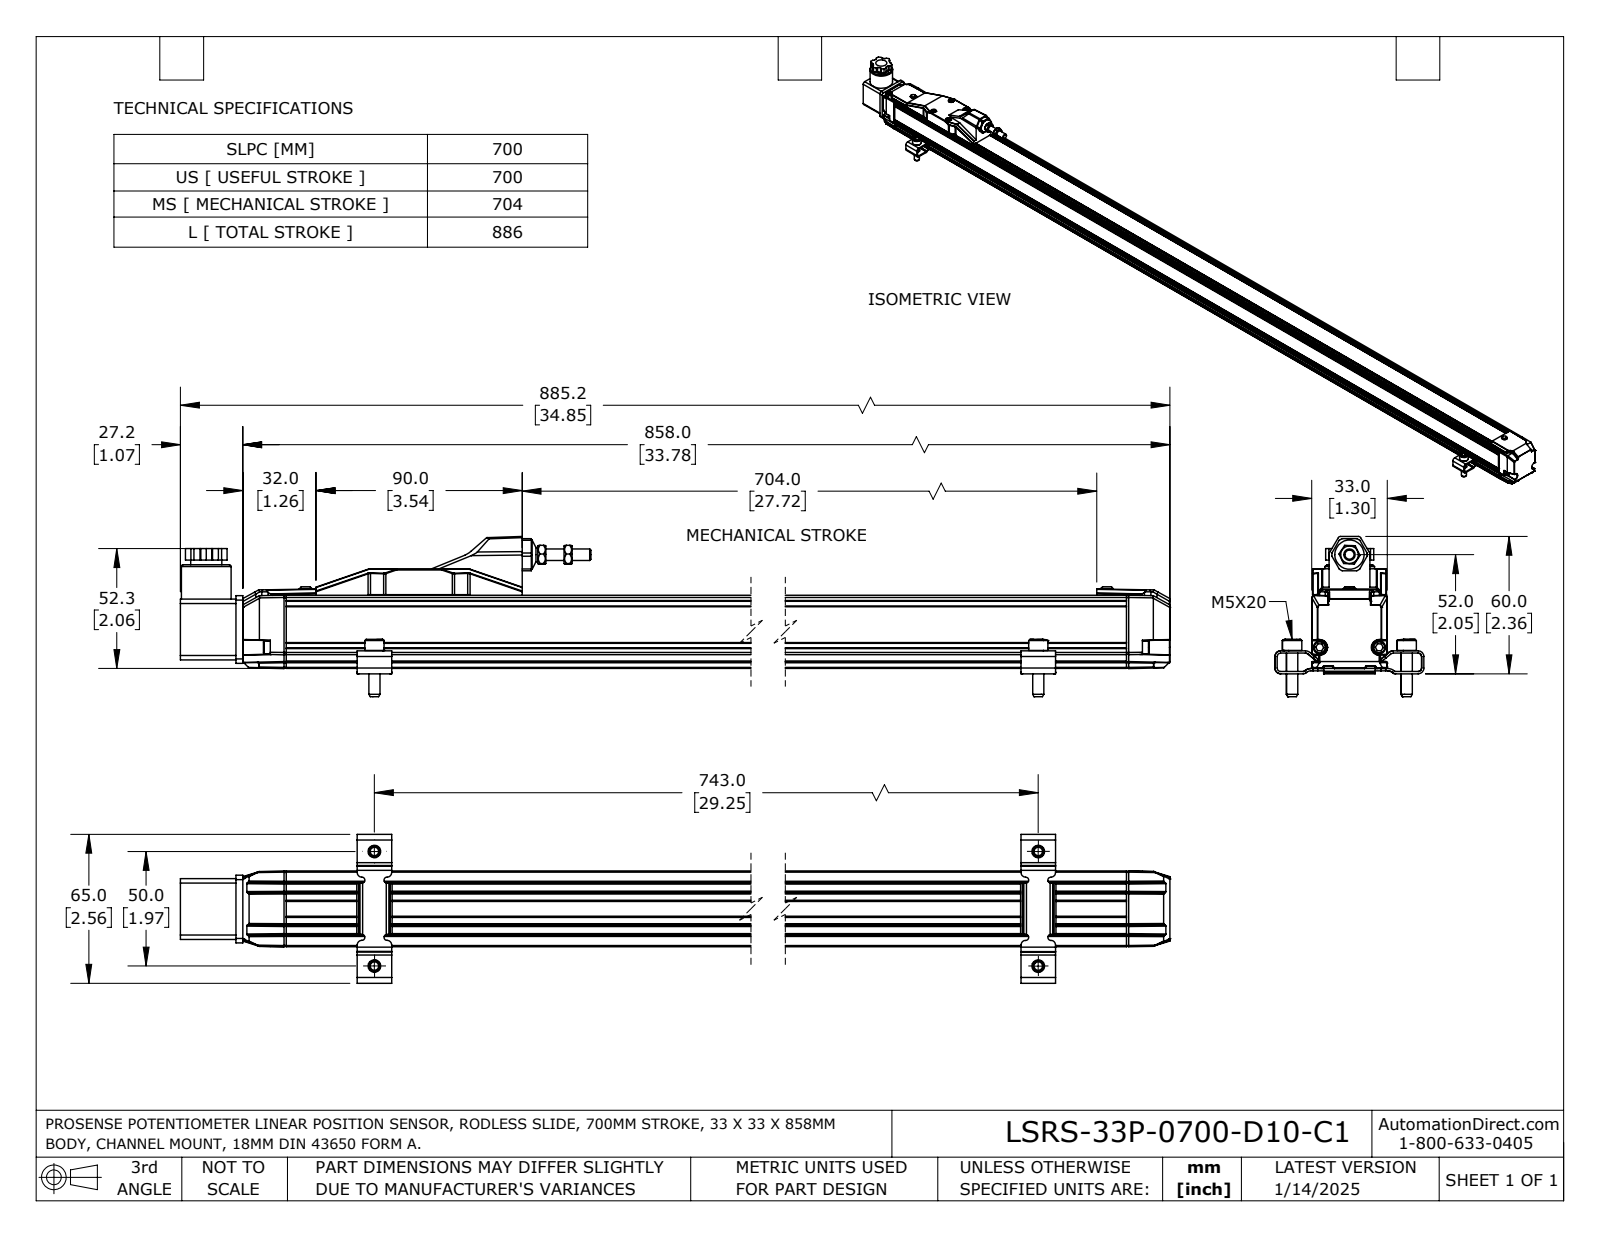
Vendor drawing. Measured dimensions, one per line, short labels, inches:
name: LSRS-33P-0700-D10-C1
written by: SolidWorks 2023 (AUTOMOTIVE_DESIGN)
unit: in
bodies: 11 solids, 1314 faces (823 planar, 359 cylindrical, 132 other)
size: 34.85 × 2.754 × 2.559
volume: 51.24 in³; area: 307.1 in²
holes: 4× ⌀0.185, 4× ⌀0.217, 2× ⌀0.106, 2× ⌀0.13, 1× ⌀0.157, 1× ⌀0.197, 1× ⌀0.209, 1× ⌀0.232, 1× ⌀0.236, 1× ⌀0.276, 1× ⌀0.394, 1× ⌀0.413
bosses: 4× ⌀0.331, 4× ⌀0.193, 4× ⌀0.181, 4× ⌀0.113, 2× ⌀0.22, 2× ⌀0.217, 2× ⌀0.118, 2× ⌀0.098
rounds: 78× R0.02, 62× R0.008, 44× R0.079, 26× R0.118, 10× R0.039, 8× R0.051, 8× R0.059, 8× R0.157
face distances: 1.299, 0.118, 1.244, 1.167, 0.237, 1.007, 0.035, 0.014, 1.285, 0.443
hole spacings: 0.597, 0.787, 0.933, 1.221, 1.286, 1.673, 1.969, 28.095
